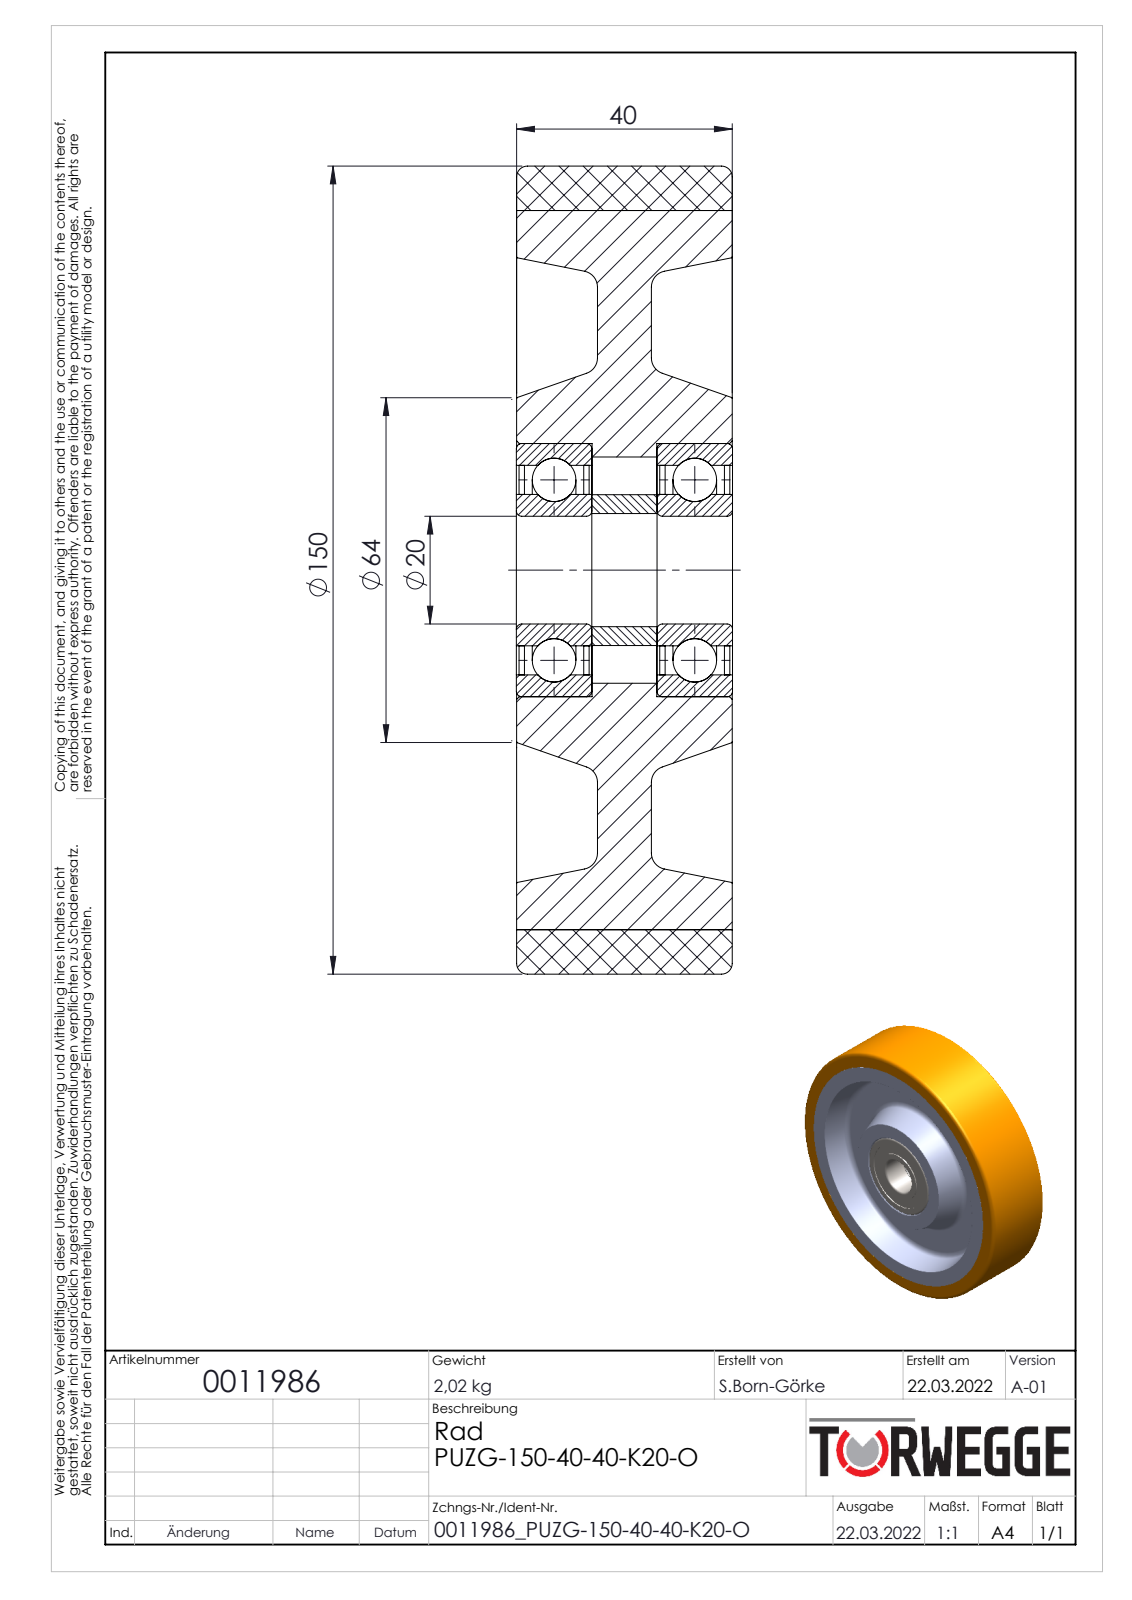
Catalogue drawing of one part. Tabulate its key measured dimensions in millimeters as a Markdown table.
| quantity | value |
| --- | --- |
| part name | 0011986 |
| STEP written by | SolidWorks 2020 (AUTOMOTIVE_DESIGN) |
| units | millimeters |
| bodies | 15 solids, 164 faces (36 planar, 60 cylindrical, 68 other) |
| overall size | 150 × 150 × 40.1 |
| volume | 492 059 mm³ |
| surface area | 130 589 mm² |
| round holes (diameter × count) | 20 × 1, 21 × 1, 28.1 × 1, 38.9 × 1, 42 × 1, 47 × 1, 133.5 × 1 |
| round bosses / shafts (diameter × count) | 150 × 1, 28 × 1 |
| partial cylindrical surfaces (radius × count) | 16.07 × 1, 17.43 × 1 |
| main face-to-face distances | 15, 25, 40, 10, 26.1, 1, 12, 13.55, 12.55, 26.05 |
